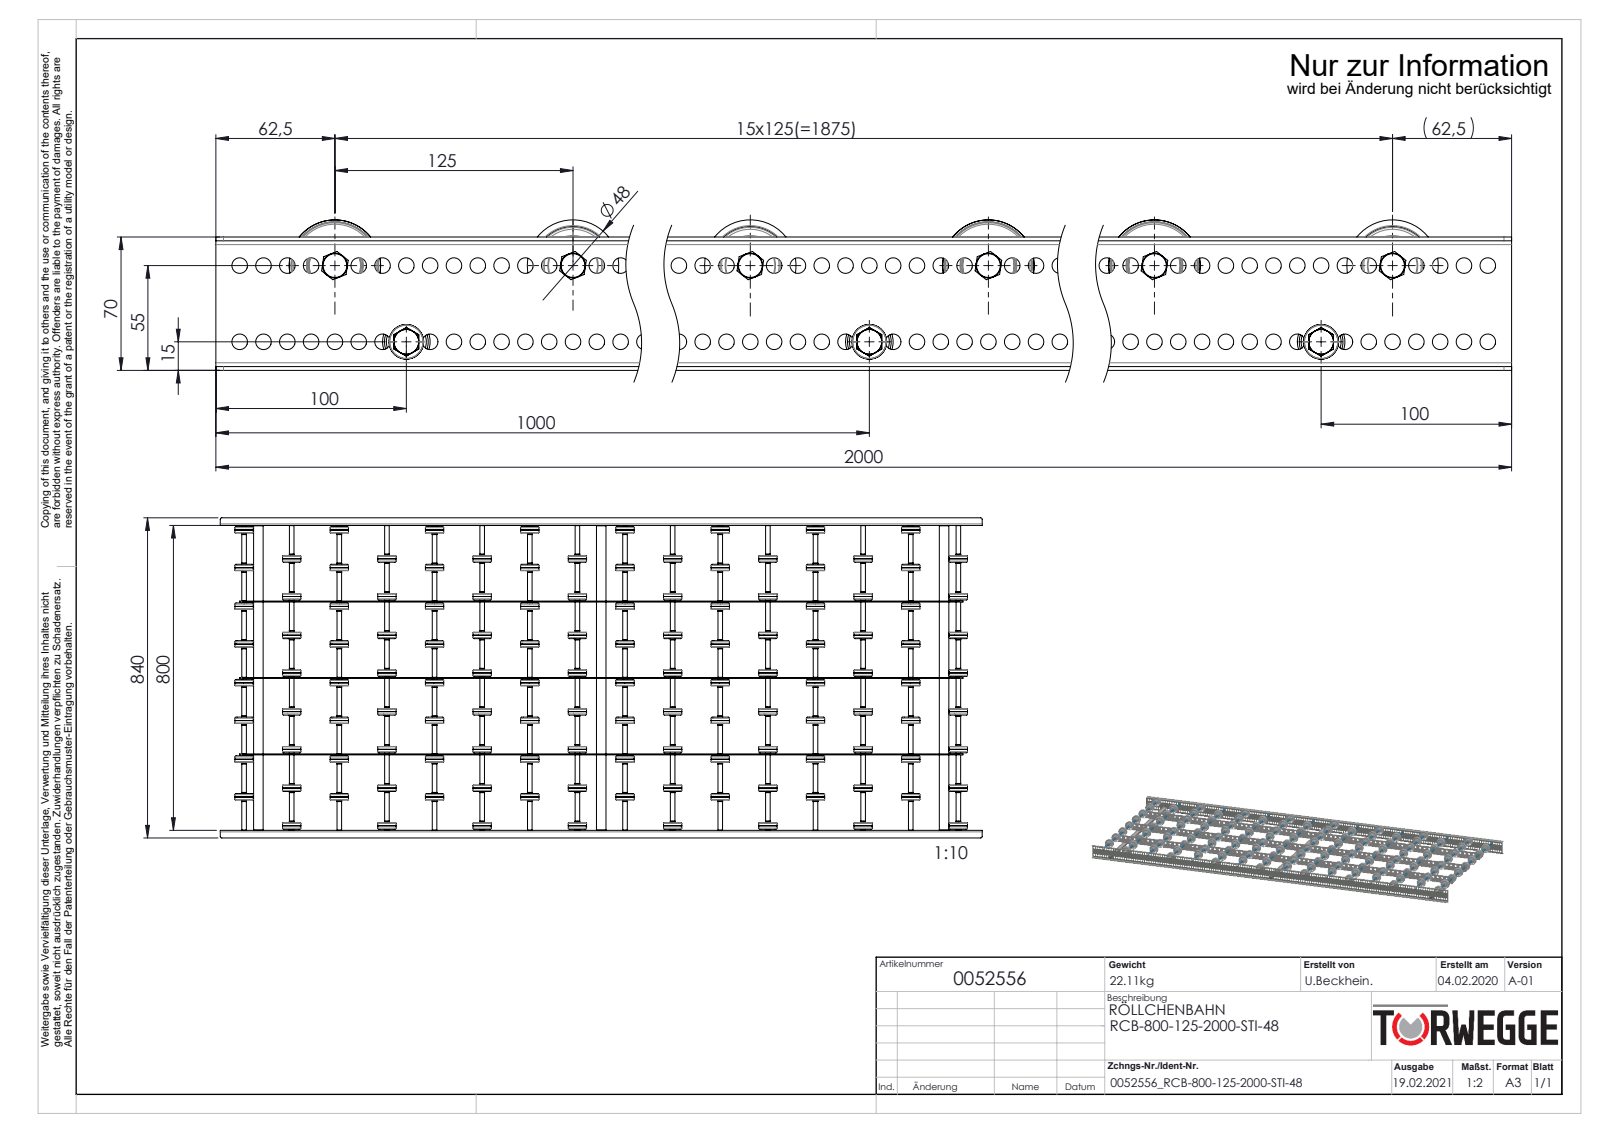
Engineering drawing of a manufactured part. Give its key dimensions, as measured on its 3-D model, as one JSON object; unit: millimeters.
{"part_name": "0046278_KB-ROHR-12X1,75mm_KFG_L75; Röllchenachse-für-Konfiguration_EL800 Stahl; Hutmutter_DIN_1587_M8; Profil_LRB-20x70x20x2_KFG_S100202_U-PROFIL-20-70-20-2-LRB-L=2000 (+6 more)", "step_written_by": "SolidWorks 2020 (AUTOMOTIVE_DESIGN)", "units": "millimeters", "bodies": {"solids": 452, "faces": 14184, "planar": 2772, "cylindrical": 5816, "other": 5596}, "overall_size": [2000, 840, 79], "volume_mm3": 5469000, "surface_area_mm2": 4263000, "round_holes": [[8.2, 318], [8.5, 76], [6.65, 16], [8, 16], [9.65, 16], [15, 16], [41, 16], [6.8, 3], [21, 3]], "round_bosses_or_shafts": [[48, 16], [13, 16], [12.5, 16], [12.4, 16], [12, 16], [11.5, 16], [25, 3], [8, 3]], "partial_cylinders_radius": [[4, 8], [2, 4], [5, 4]], "face_to_face_distances": [200.5, 401, 2, 203, 2.5, 198, 802, 601.5, 403.5, 398.5], "hole_center_spacings": [12.5, 25, 37.5, 50, 62.5, 75, 87.5, 100]}
